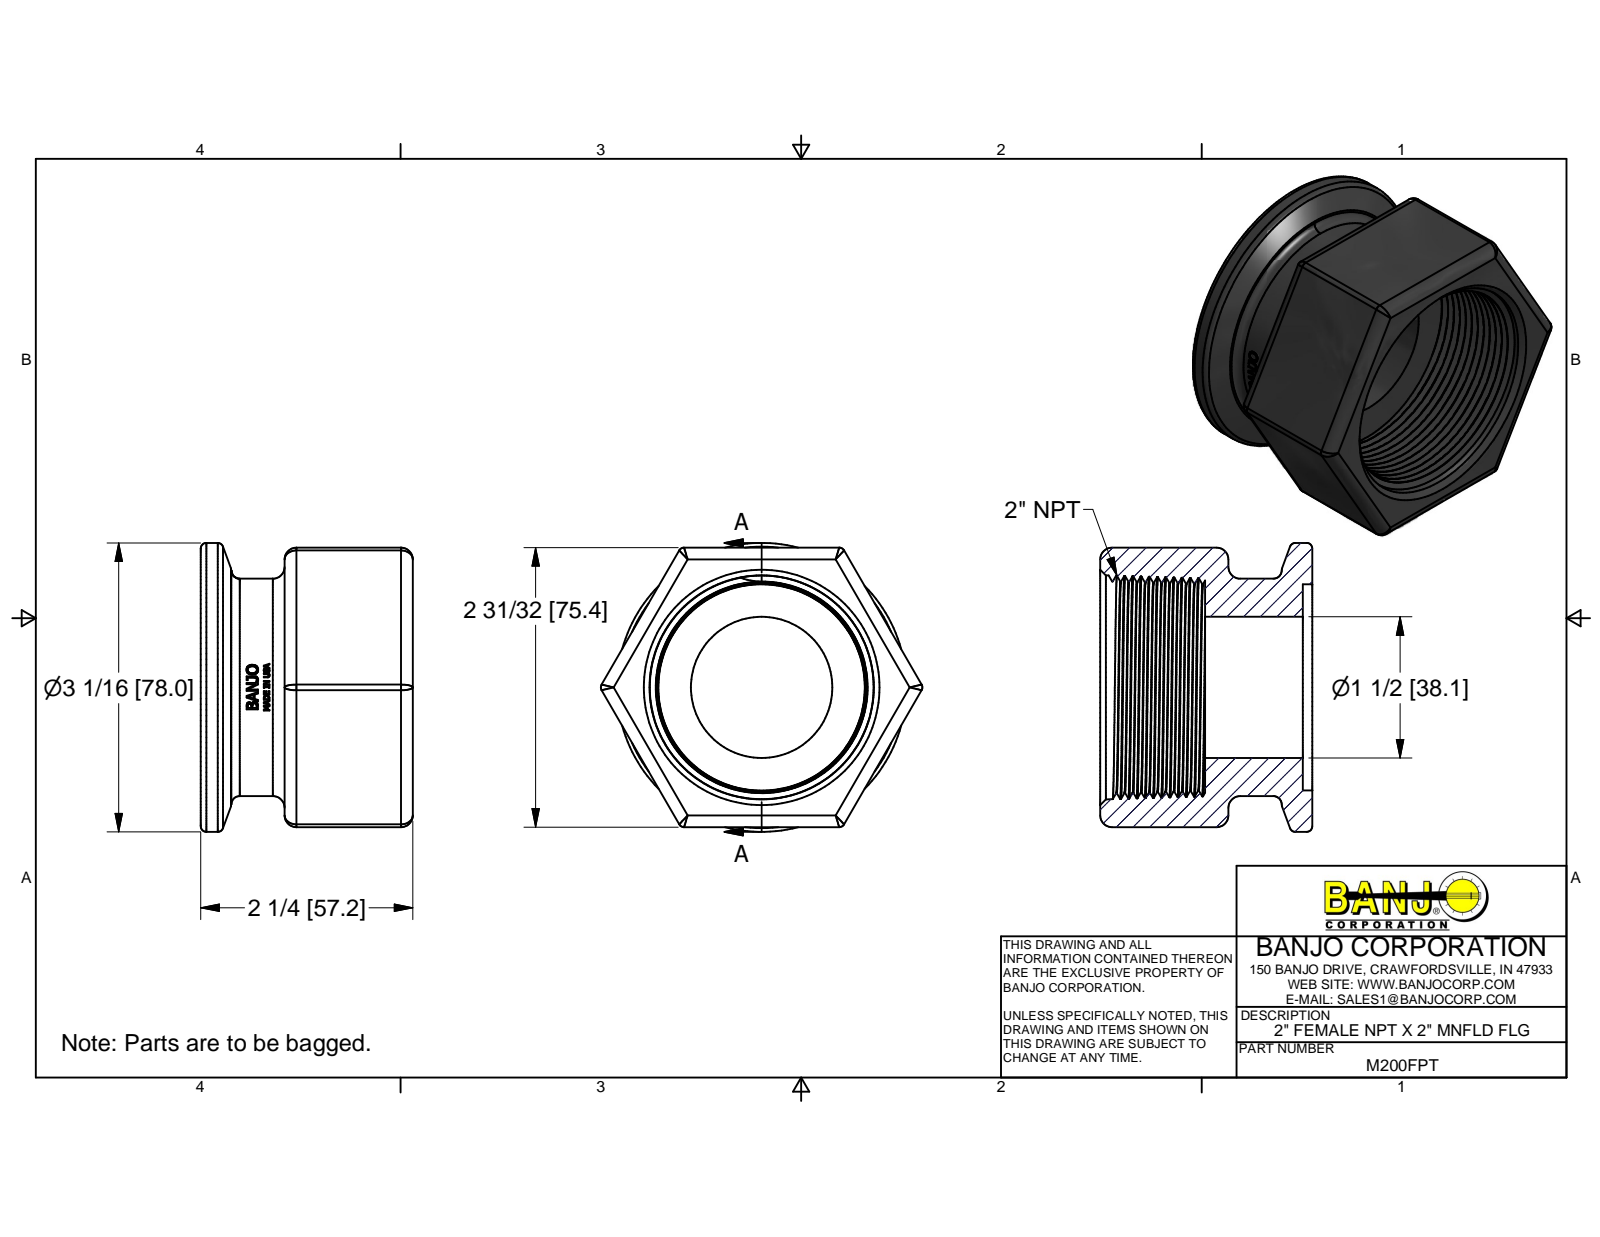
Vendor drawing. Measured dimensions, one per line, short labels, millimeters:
name: M200FPT
written by: Autodesk Inventor 2014 (AUTOMOTIVE_DESIGN)
unit: mm
bodies: 1 solid, 377 faces (179 planar, 54 cylindrical, 144 other)
size: 86.64 × 77.98 × 57.15
volume: 133 670 mm³; area: 35 798 mm²
holes: 1× ⌀38.1, 1× ⌀55.63
bosses: 1× ⌀77.98, 1× ⌀58.67
rounds: 12× R3.17, 6× R1.52, 1× R16.73, 1× R28.57
face distances: 75.44, 28.88, 26.34, 2.54, 28.27, 54.61, 57.15, 6.27, 34.54, 20.07
